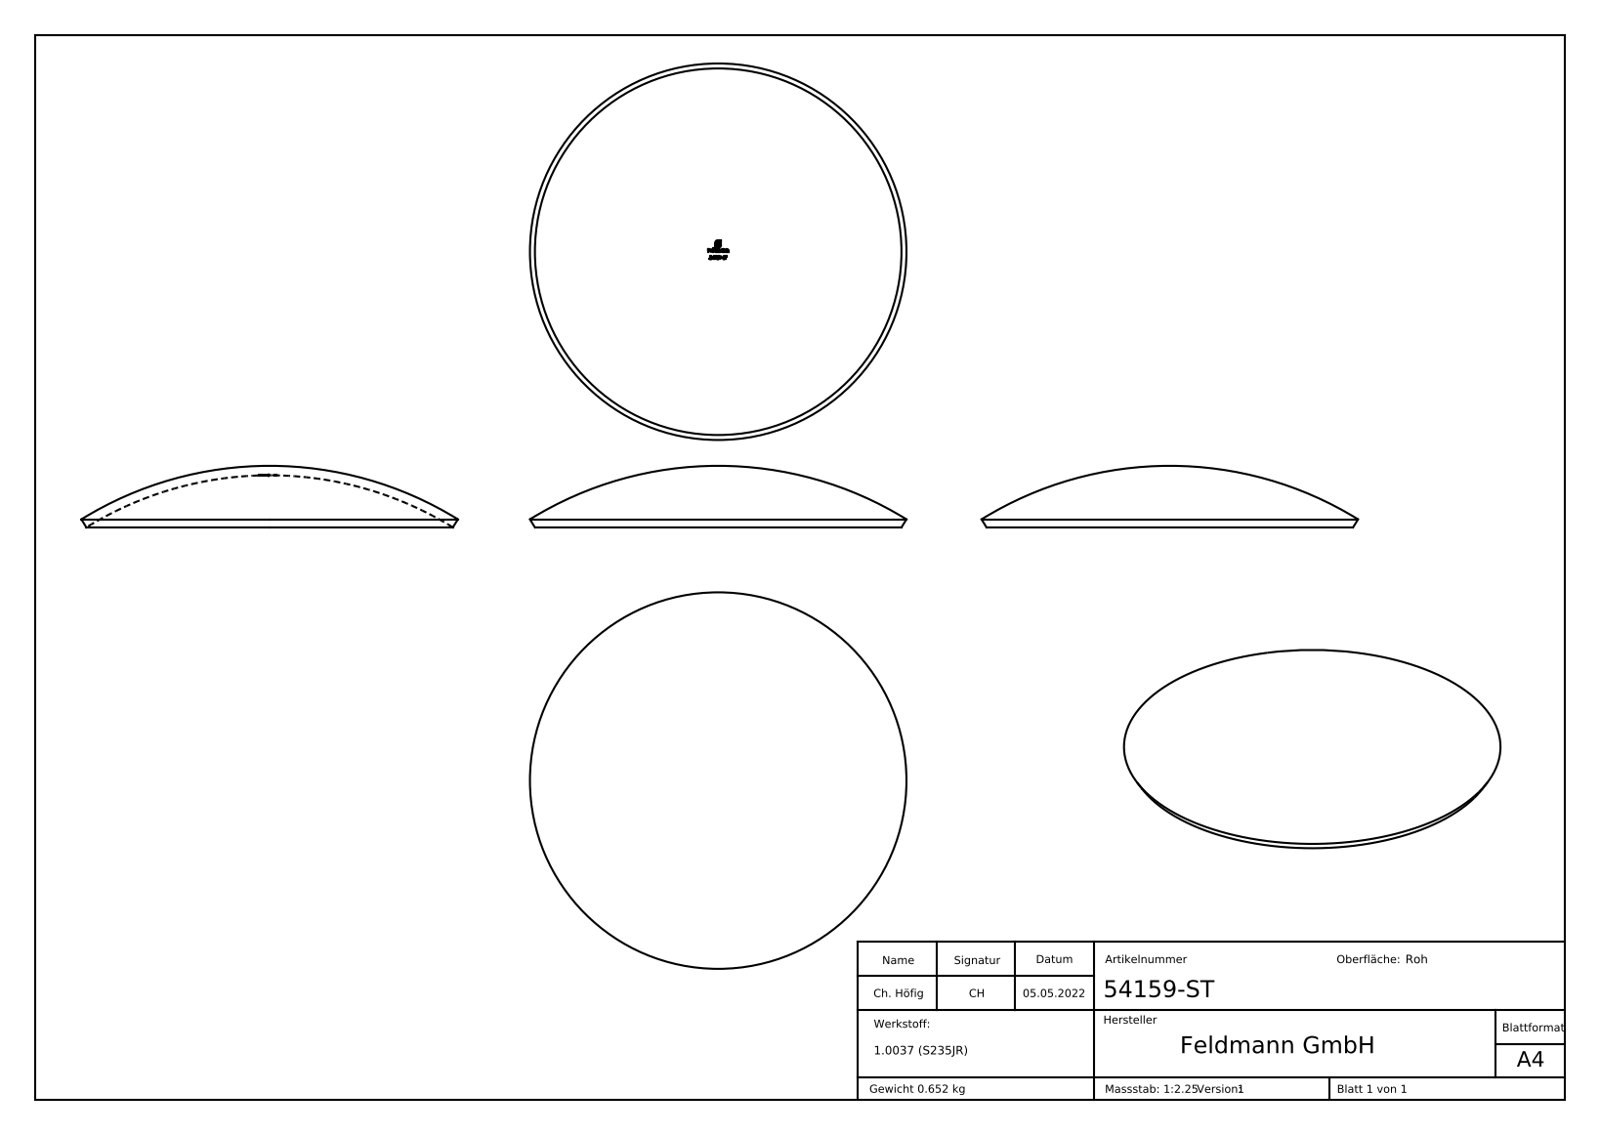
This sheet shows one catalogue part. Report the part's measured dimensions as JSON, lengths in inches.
{"part_name": "54159-ST", "step_written_by": "SolidWorks 2018 (CONFIG_CONTROL_DESIGN)", "units": "inches", "bodies": {"solids": 1, "faces": 257, "planar": 124, "cylindrical": 0, "other": 133}, "overall_size": [6.26, 6.26, 1.024], "volume_in3": 5.101, "surface_area_in2": 67.86, "face_to_face_distances": [0.167, 0.034, 0.05, 0.045, 0.023, 0.042, 0.027, 0.025, 0.126, 0.013]}
